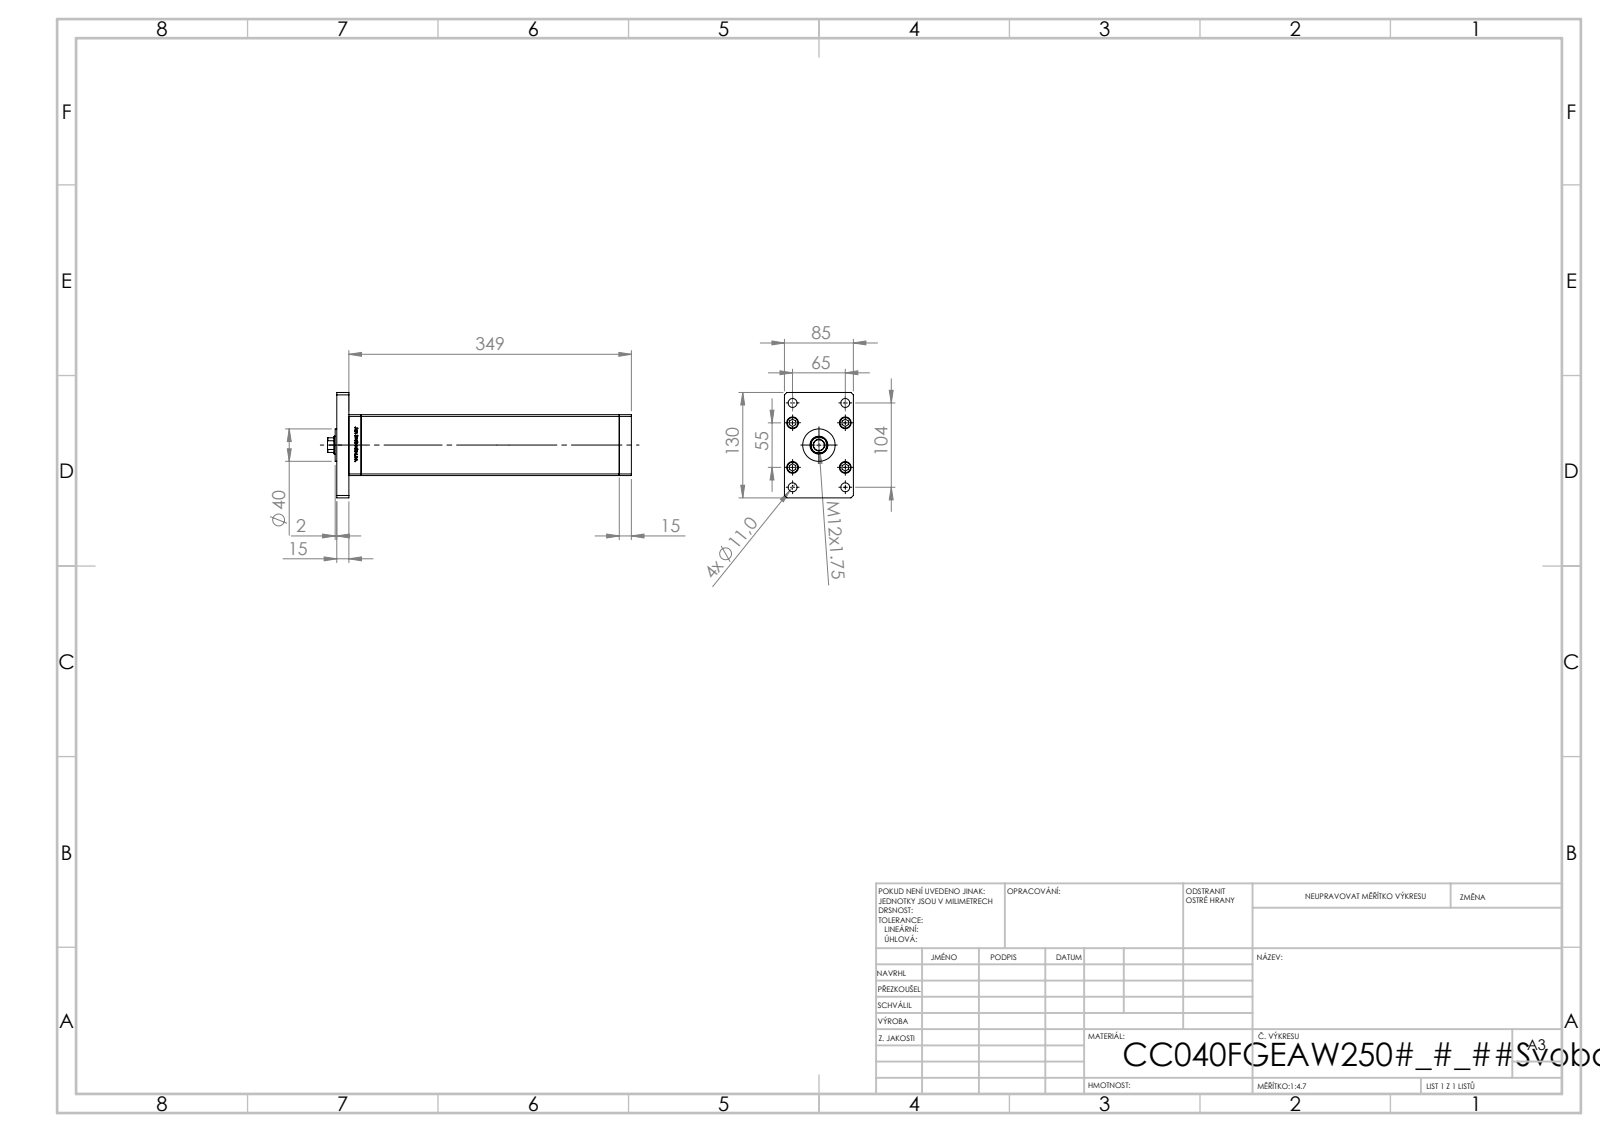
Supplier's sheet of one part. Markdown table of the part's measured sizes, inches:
| quantity | value |
| --- | --- |
| part name | ALLEN BOLT; V220C_F_MIDDLE; V220C_F; V220C BACK_F (+2 more) |
| STEP written by | SolidWorks 2019 (CONFIG_CONTROL_DESIGN) |
| units | inches |
| bodies | 19 solids, 1310 faces (517 planar, 187 cylindrical, 606 other) |
| overall size | 14.764 × 5.118 × 3.346 |
| volume | 126.1 in³ |
| surface area | 449.1 in² |
| round holes (diameter × count) | 0.433 × 9, 0.61 × 5, 0.394 × 4, 0.571 × 4, 0.079 × 2, 0.518 × 2, 0.531 × 1, 0.866 × 1, 0.925 × 1 |
| round bosses / shafts (diameter × count) | 0.315 × 9, 0.571 × 5, 1.575 × 1 |
| partial cylindrical surfaces (radius × count) | 0.037 × 2, 0.413 × 1 |
| main face-to-face distances | 3.346, 0.591, 2.953, 13.13, 13.72, 1.181, 12.539, 0.413, 14.311, 2.539 |
| hole center spacings | 1.102, 0.965, 1.676, 2.414, 2.559, 2.735, 3.13, 4.043 |
